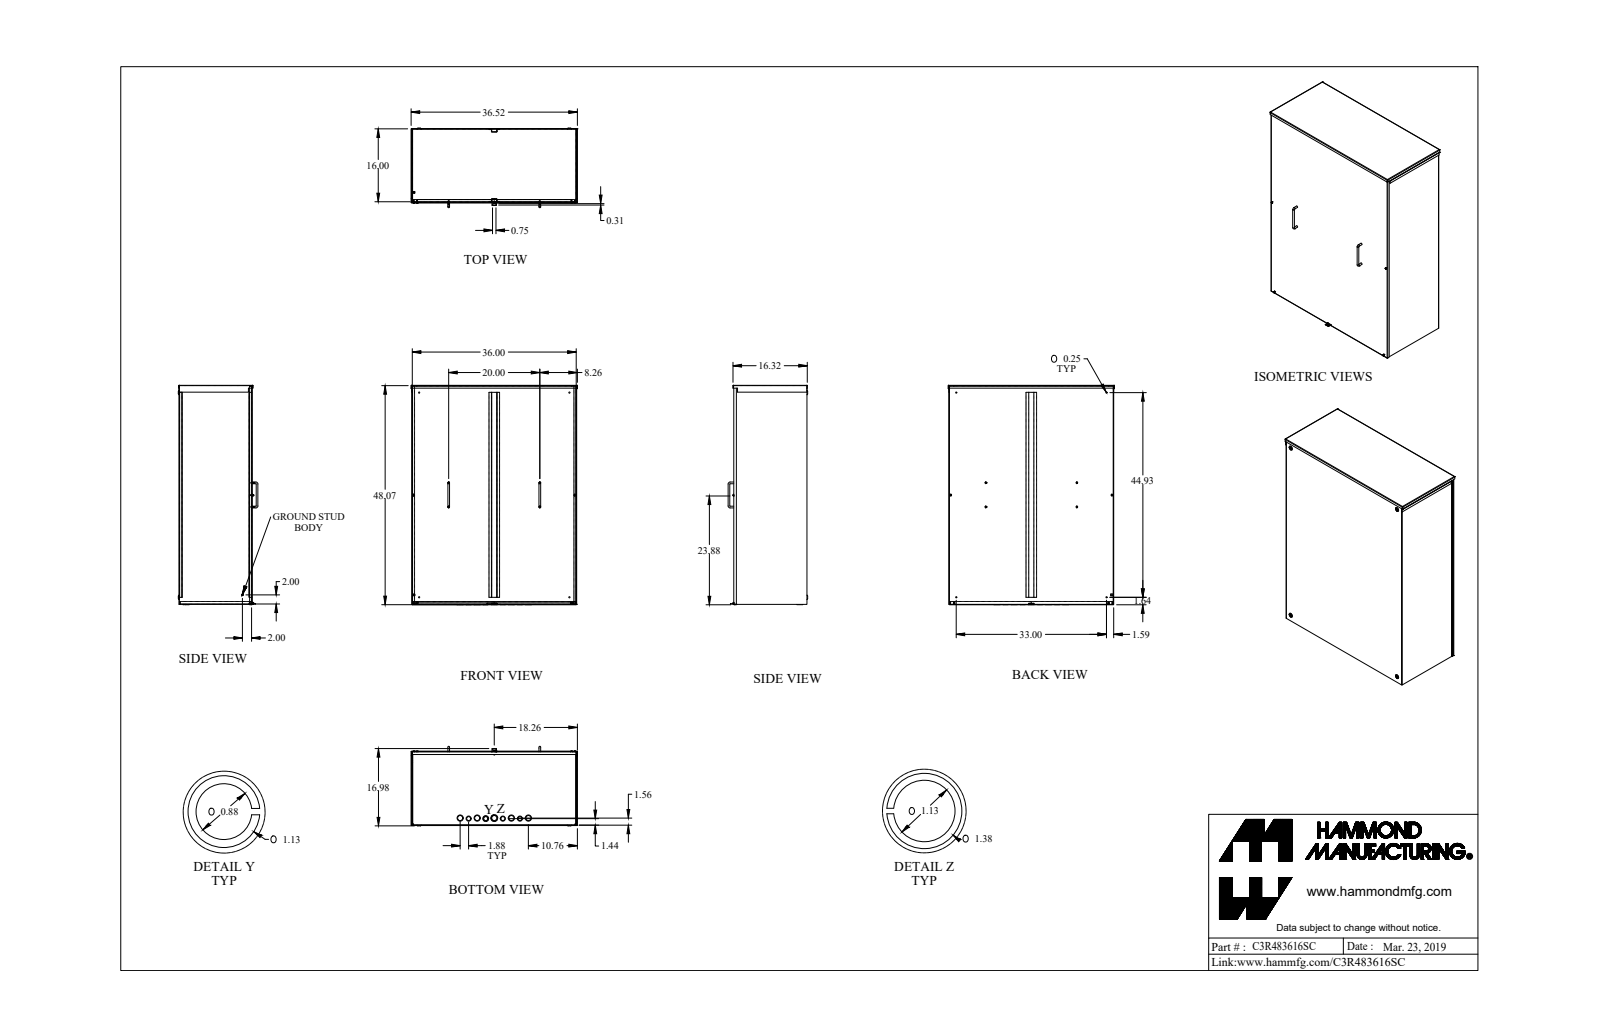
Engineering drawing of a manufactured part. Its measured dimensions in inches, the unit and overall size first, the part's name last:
Units: inches
Overall size (bounding box): 48.171 × 36.519 × 17.478
Round holes (diameter × count): ⌀0.156 ×5, ⌀0.17 ×4, ⌀0.203 ×4, ⌀0.25 ×4, ⌀1.125 ×3, ⌀0.875 ×2, ⌀0.875 ×2, ⌀1.125 ×2, ⌀0.125 ×1, ⌀0.137 ×1
Round bosses / shafts (diameter × count): ⌀0.375 ×11, ⌀0.19 ×8, ⌀1.125 ×4, ⌀0.367 ×4, ⌀1.375 ×3, ⌀1.375 ×2, ⌀0.125 ×1
Partial cylindrical surfaces — rounded edges, fillets, slot ends (radius × count): R0.036 ×28, R0.108 ×28, R0.109 ×8, R0.125 ×8, R0.156 ×2, R0.029 ×1, R0.086 ×1
Main face-to-face distances: 0.072, 16, 15.928, 16.072, 35.928, 48, 36, 35.856, 48.072, 47.928
Hole centre spacings: 20, 3.75, 7.5, 0.024, 1.879, 1.88, 5.3, 20.69
Volume: 484.8 in³ · Surface area: 13 499 in²
Bodies: 19 solids, 653 faces (342 planar, 193 cylindrical, 118 other)
Part name (STEP PRODUCT): C3R483616SC_Default
STEP written by: SolidWorks 2019 (CONFIG_CONTROL_DESIGN)
